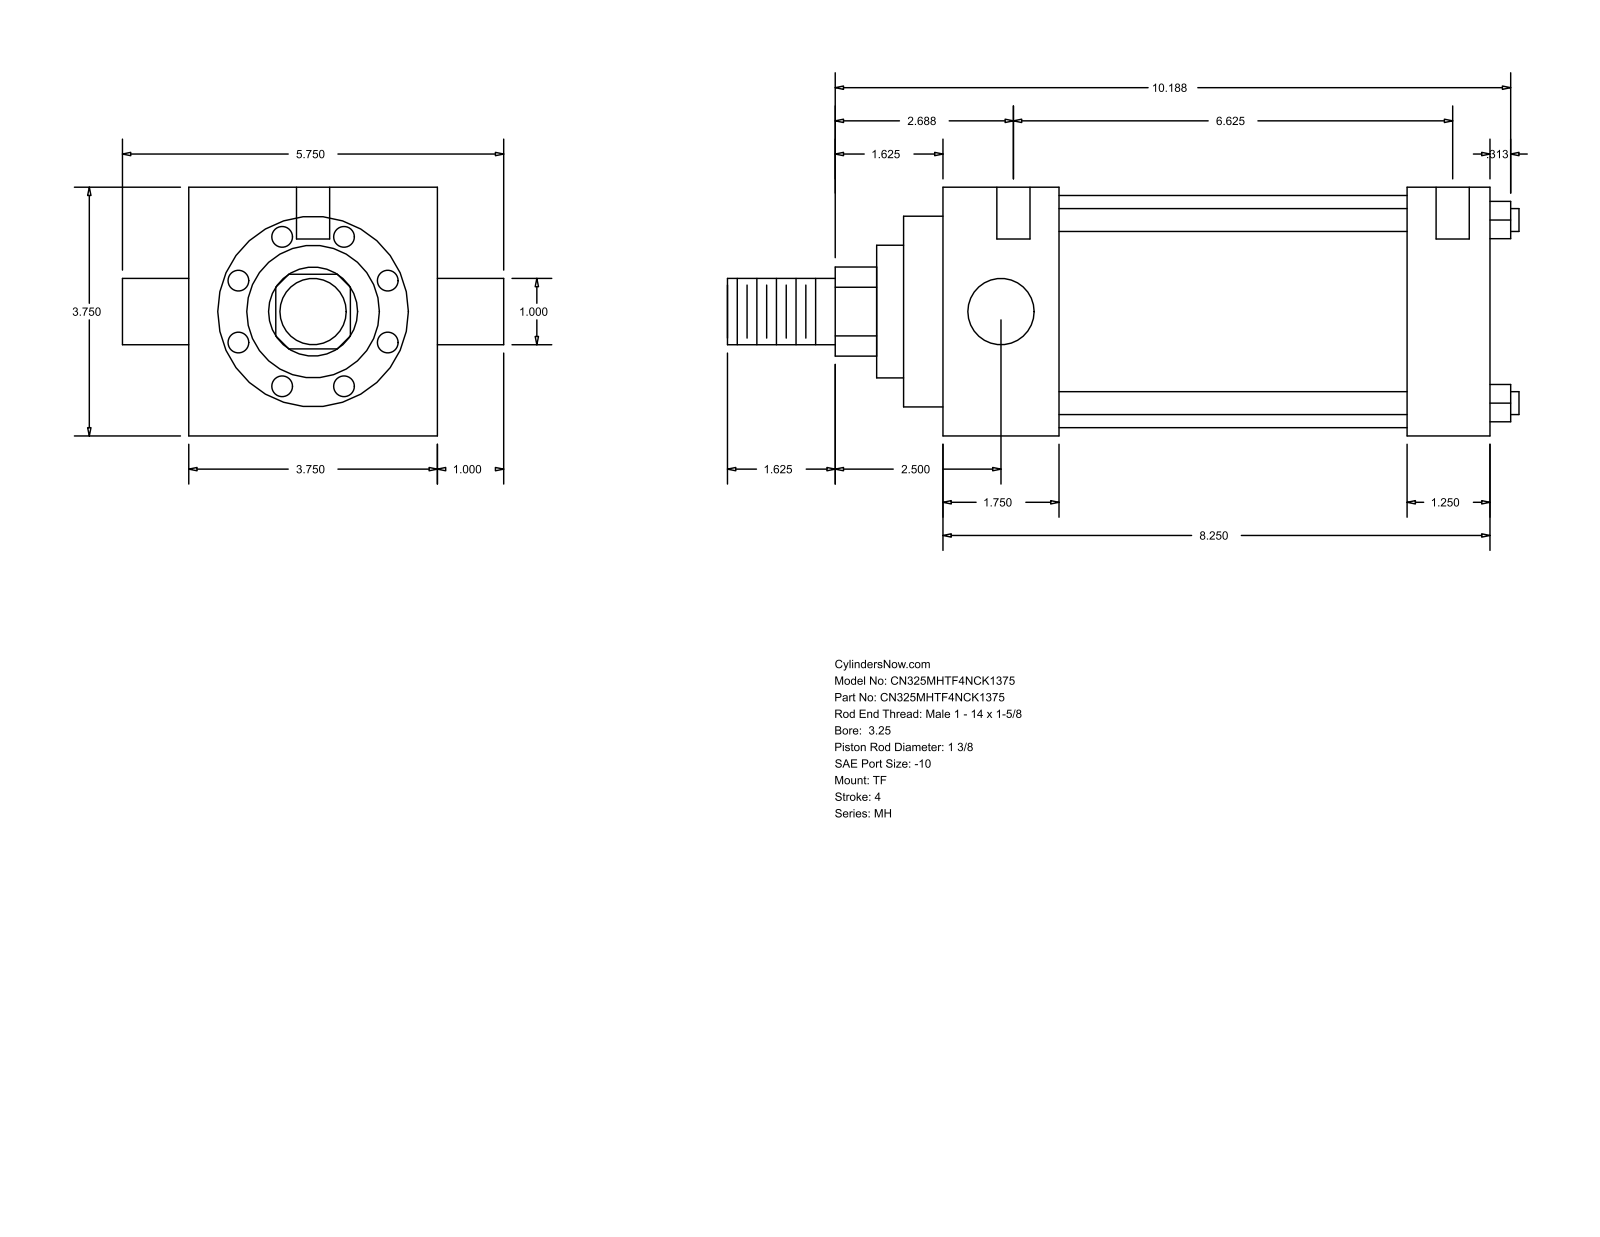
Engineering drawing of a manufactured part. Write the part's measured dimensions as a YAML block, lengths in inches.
part_name: "MH_TF__0325_1.375"
step_written_by: "GSSL Pune (CONFIG_CONTROL_DESIGN)"
units: inches
bodies: {solids: 0, faces: 86, planar: 61, cylindrical: 25, other: 0}
overall_size: [11.937, 5.75, 3.75]
round_holes:
  - {diameter: 0.219, count: 3}
  - {diameter: 0.5, count: 2}
round_bosses_or_shafts:
  - {diameter: 0.345, count: 4}
  - {diameter: 1, count: 2}
  - {diameter: 3.5, count: 1}
  - {diameter: 2.875, count: 1}
  - {diameter: 2, count: 1}
  - {diameter: 1.375, count: 1}
partial_cylinders:
  - {radius: 0.672, count: 1}
face_to_face_distances: [3.75, 8.25, 1.75, 7, 5.25, 6.5, 1.25, 0.594, 2.344, 7.594]
hole_center_spacings: [0.063, 0.187, 6.625, 6.688, 6.813, 6.875]
